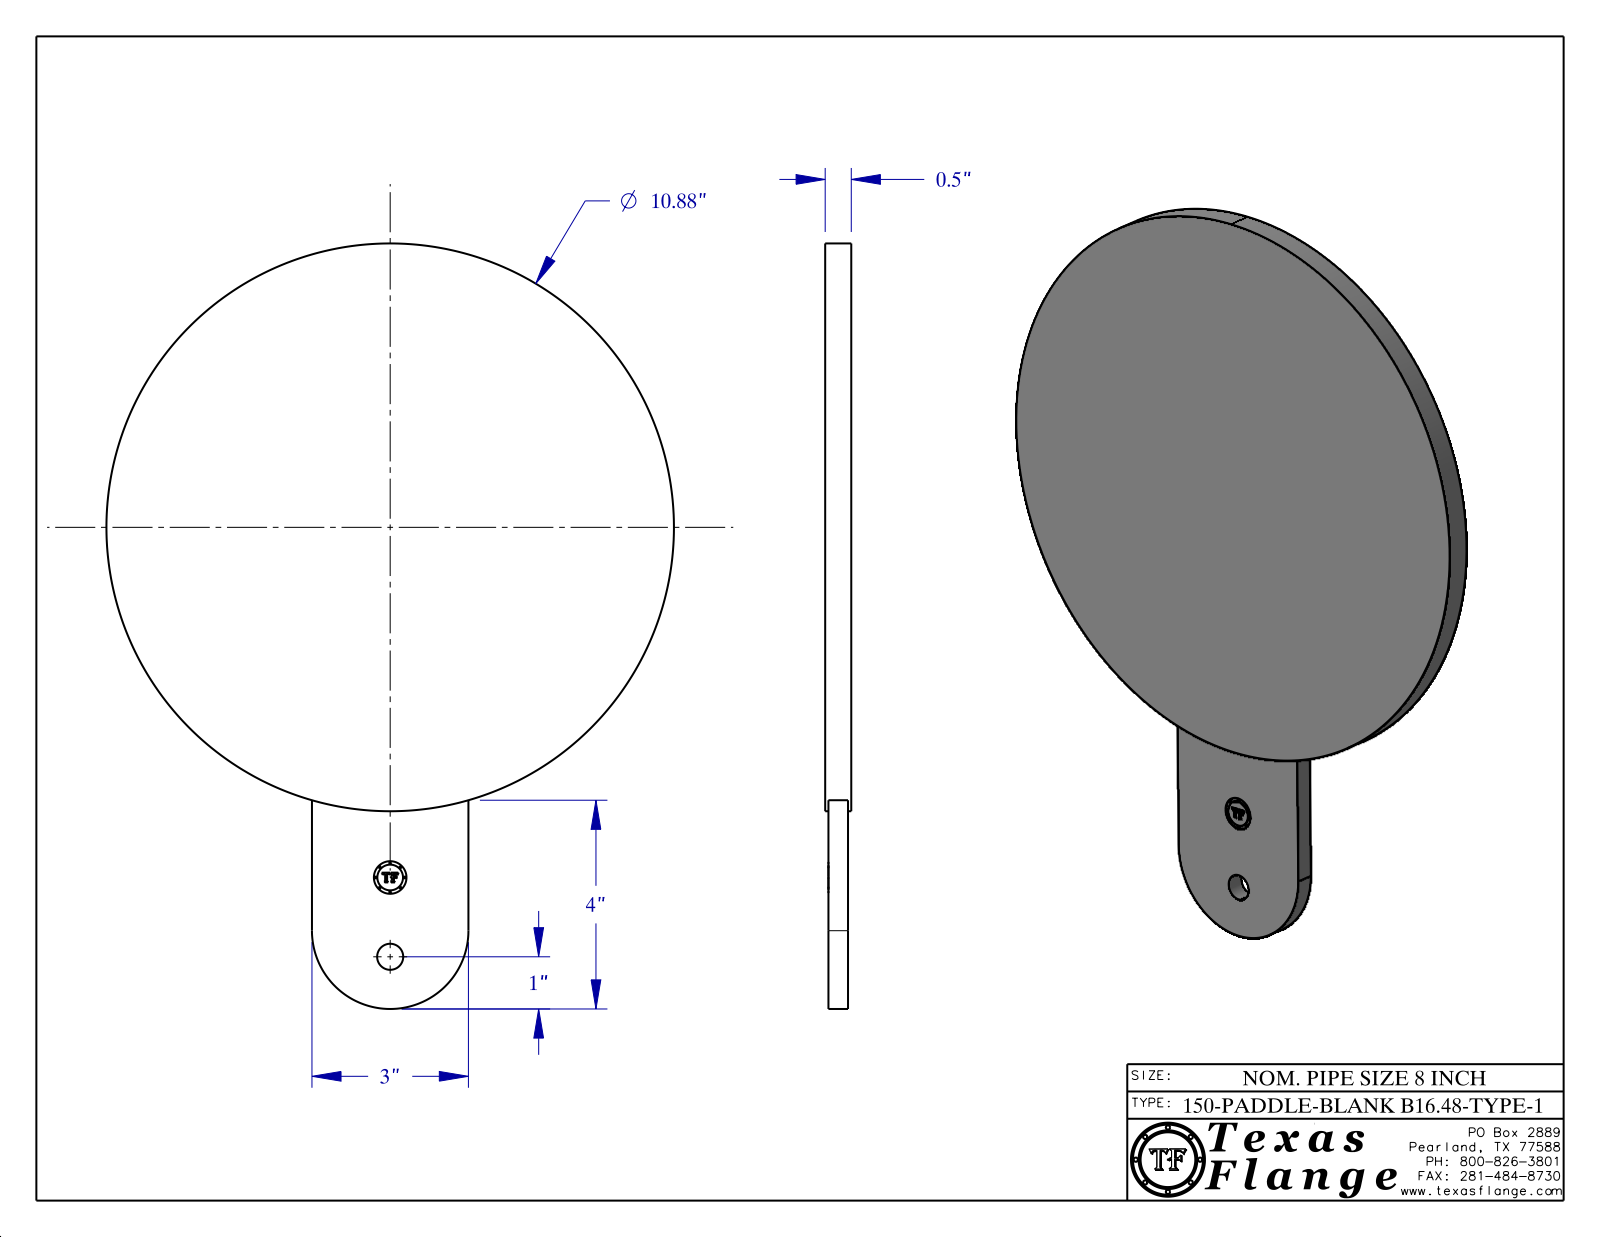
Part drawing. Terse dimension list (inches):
name: 8-150-PADDLE-BLANK-B16.48-TYPE-1
written by: CATIA V5 STEP AP214 (AUTOMOTIVE_DESIGN)
unit: in
bodies: 1 solid, 396 faces (371 planar, 25 cylindrical, 0 other)
size: 14.669 × 10.88 × 0.5
volume: 50.39 in³; area: 227.1 in²
holes: 1× ⌀0.5, 1× ⌀0.625
bosses: 8× ⌀0.038, 1× ⌀10.88, 1× ⌀0.492
rounds: 1× R1.5
face distances: 0.5, 0.063, 0.437, 0.375, 3, 0.422, 0.36, 0.015, 0.078, 1.437
hole spacings: 1.52
